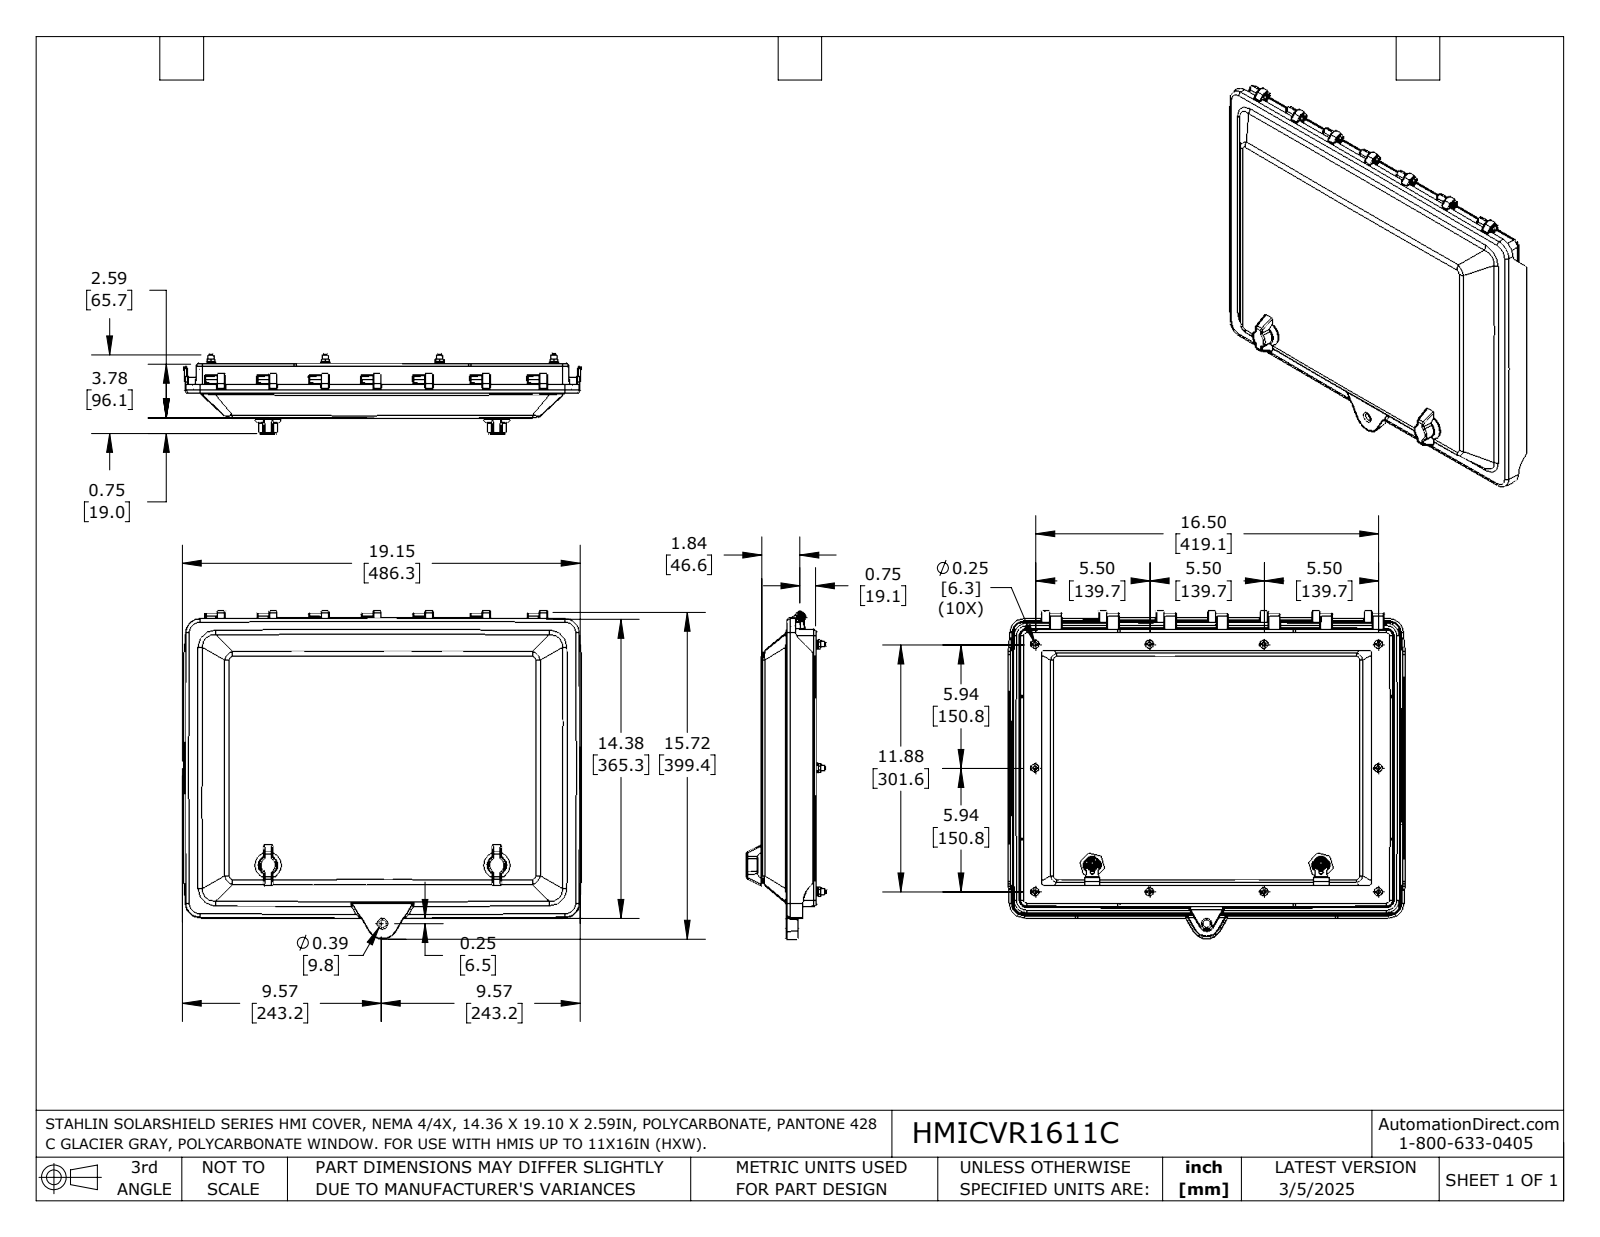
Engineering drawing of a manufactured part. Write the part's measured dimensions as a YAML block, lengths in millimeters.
part_name: "HMICVR1611C"
step_written_by: "SolidWorks 2024 (AUTOMOTIVE_DESIGN)"
units: millimeters
bodies: {solids: 55, faces: 2581, planar: 857, cylindrical: 643, other: 1081}
overall_size: [486.3, 399.4, 97.3]
volume: 1221000
surface_area: 693500
round_holes:
  - {diameter: 5, count: 12}
  - {diameter: 6.4, count: 10}
  - {diameter: 4.8, count: 9}
  - {diameter: 4.3, count: 2}
  - {diameter: 6, count: 2}
  - {diameter: 8, count: 2}
  - {diameter: 15, count: 2}
  - {diameter: 21.5, count: 2}
  - {diameter: 2.1, count: 1}
  - {diameter: 5.1, count: 1}
  - {diameter: 8.3, count: 1}
  - {diameter: 9.4, count: 1}
round_bosses_or_shafts:
  - {diameter: 10, count: 10}
  - {diameter: 9.5, count: 10}
  - {diameter: 5.1, count: 10}
  - {diameter: 32, count: 2}
  - {diameter: 19.8, count: 2}
  - {diameter: 13.5, count: 2}
  - {diameter: 5.5, count: 2}
  - {diameter: 4.8, count: 2}
partial_cylinders:
  - {radius: 0.5, count: 120}
  - {radius: 0.3, count: 61}
  - {radius: 0.8, count: 56}
  - {radius: 0.5, count: 32}
  - {radius: 1, count: 21}
  - {radius: 1.5, count: 12}
  - {radius: 2.7, count: 8}
  - {radius: 4.5, count: 6}
face_to_face_distances: [6.4, 25.4, 28.6, 31.8, 34.9, 3.2, 31.2, 24.9, 0.5, 3.7]
hole_center_spacings: [139.7, 279.4, 332.4, 70.8, 77, 150.8, 205.6, 278.2]
